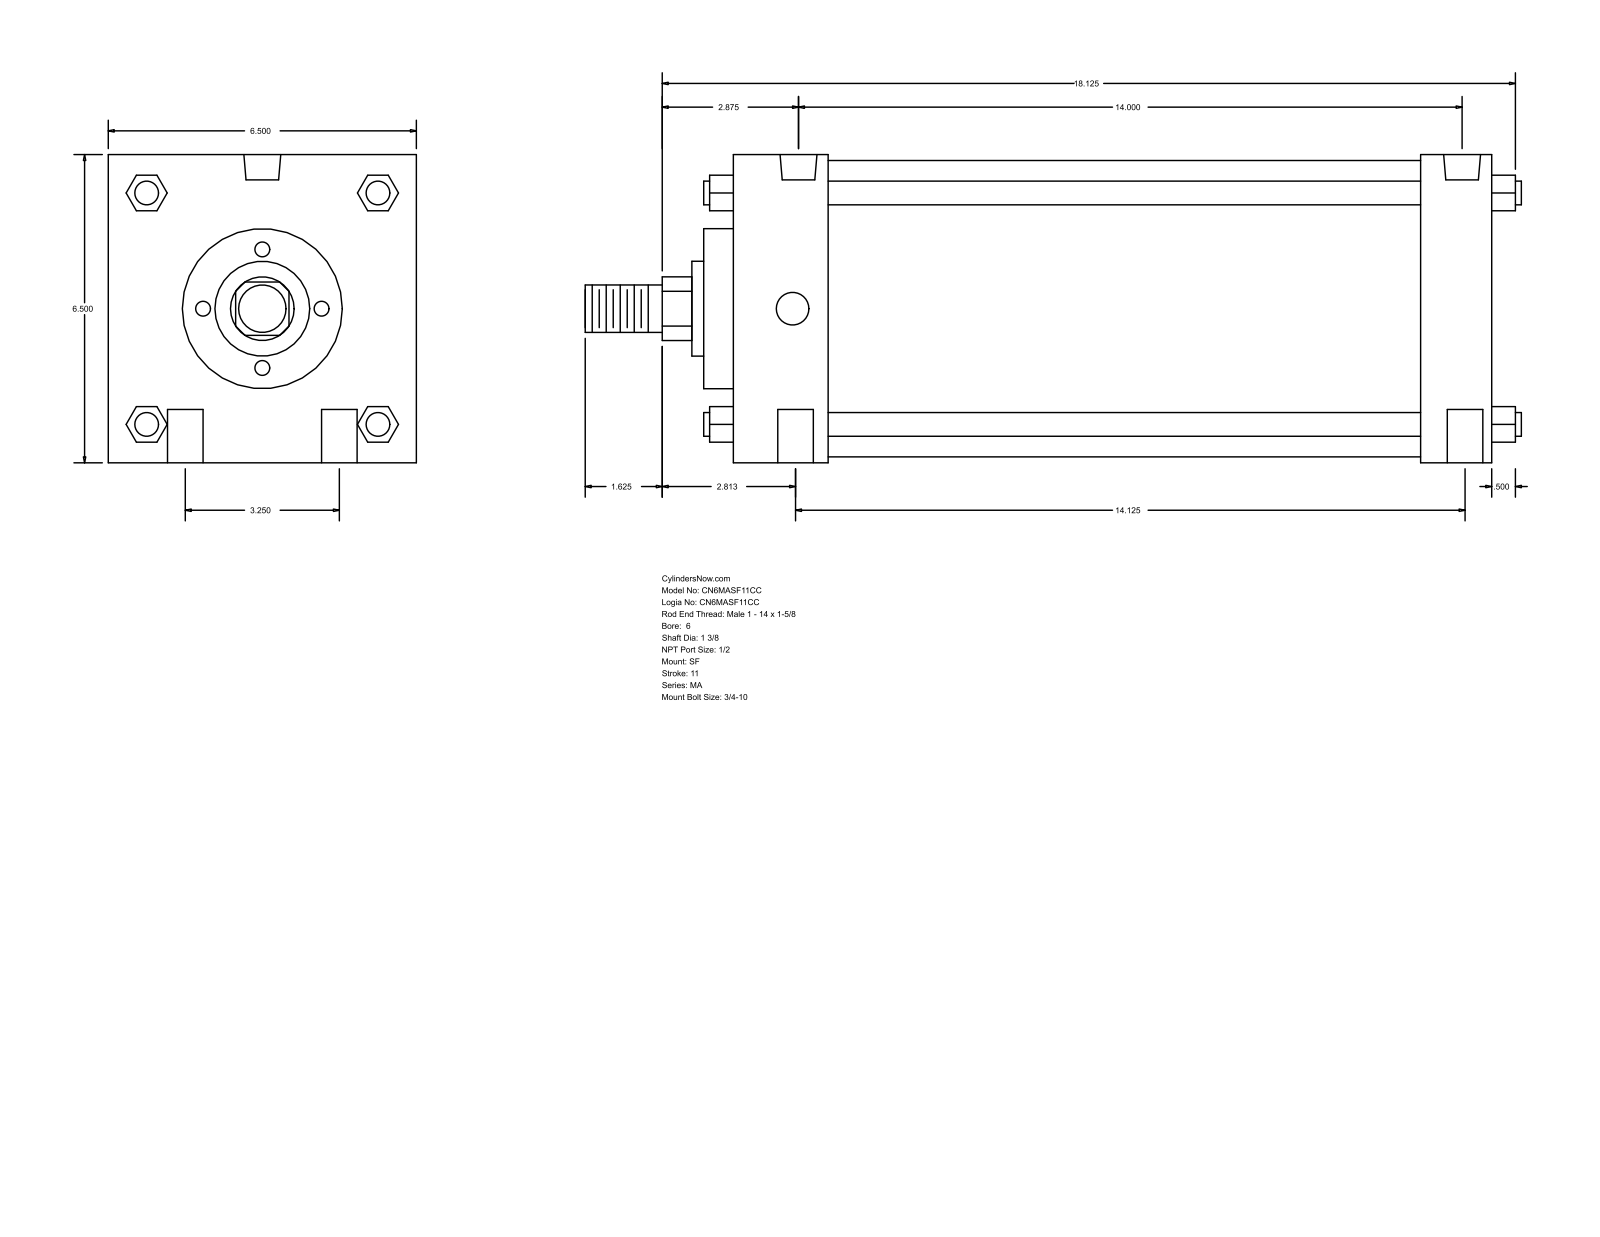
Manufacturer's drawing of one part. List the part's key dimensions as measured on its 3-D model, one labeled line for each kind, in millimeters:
Part name (STEP PRODUCT): MA_SF__0600_1.375
STEP written by: GSSL Pune (CONFIG_CONTROL_DESIGN)
Units: millimetres
Bodies: 0 solids, 126 faces (95 planar, 31 cylindrical, 0 other)
Overall size (bounding box): 501.65 × 165.1 × 165.1
Round holes (diameter × count): ⌀19.05 ×4, ⌀17.46 ×2, ⌀19.77 ×2
Round bosses / shafts (diameter × count): ⌀12.7 ×4, ⌀158.75 ×1, ⌀85.72 ×1, ⌀50.8 ×1, ⌀34.92 ×1, ⌀25.4 ×1
Partial cylindrical surfaces — rounded edges, fillets, slot ends (radius × count): R17.06 ×1
Main face-to-face distances: 165.1, 406.4, 368.3, 50.8, 38.1, 317.5, 355.6, 66.67, 15.87, 384.17
Hole centre spacings: 41.3, 359.56, 82.54, 358.77, 368.14, 355.59, 355.6
